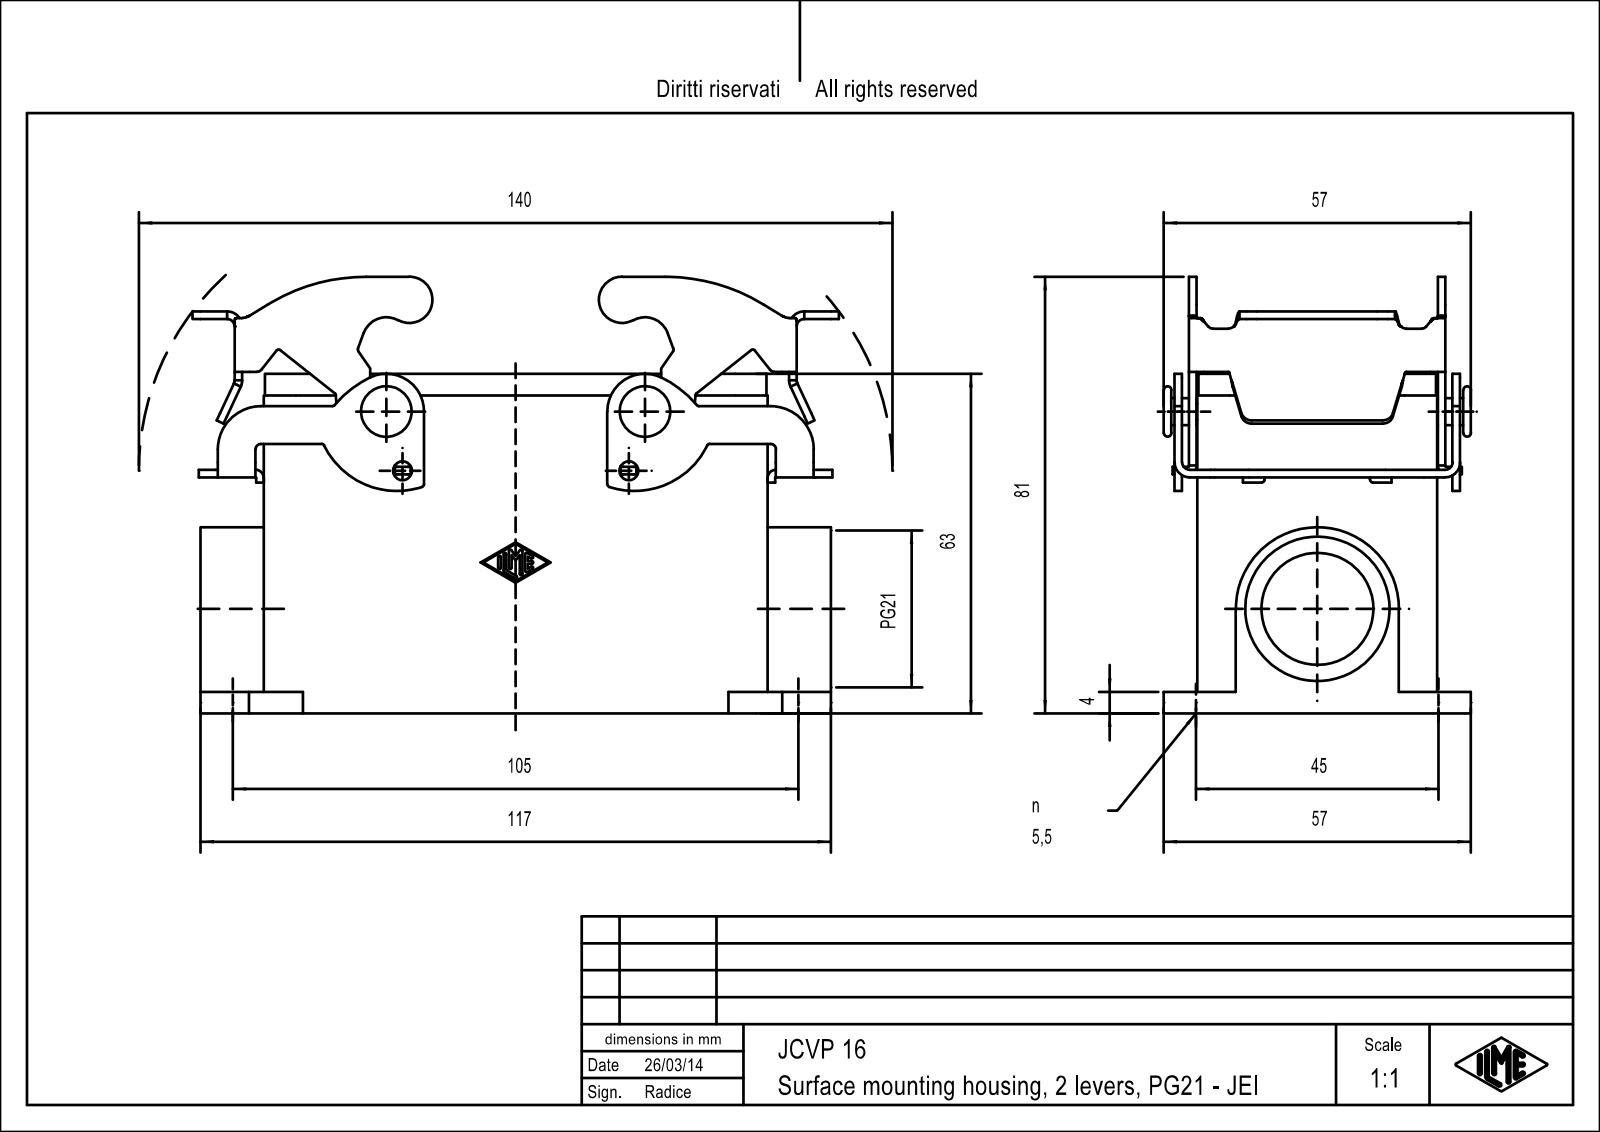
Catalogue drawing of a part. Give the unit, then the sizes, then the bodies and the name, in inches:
Units: inches
Overall size (bounding box): 4.723 × 3.189 × 2.244
Round holes (diameter × count): ⌀0.097 ×4, ⌀0.118 ×4, ⌀0.217 ×4, ⌀0.138 ×2, ⌀0.818 ×1, ⌀1.054 ×1
Round bosses / shafts (diameter × count): ⌀0.197 ×2, ⌀0.126 ×2, ⌀0.118 ×2
Partial cylindrical surfaces — rounded edges, fillets, slot ends (radius × count): R0.02 ×22, R0.039 ×18, R0.01 ×16, R0.059 ×14, R0.079 ×12, R0.055 ×10, R0.11 ×10, R0.315 ×6
Main face-to-face distances: 0.157, 1.594, 0.055, 1.752, 1.437, 0.106, 1.925, 0.061, 0.219, 1.656
Hole centre spacings: 0.647, 1.517, 3.61, 3.862, 1.063, 1.772, 3.051, 3.231
Volume: 6.8 in³ · Surface area: 97.24 in²
Bodies: 3 solids, 613 faces (293 planar, 272 cylindrical, 48 other)
Part name (STEP PRODUCT): p1; p2; p3; JCVP_16
STEP written by: Creo Elements/Direct Modeling 18.0B 02-Dec-2011 (C) Parametric Technology GmbH (AUTOMOTIVE_DESIGN)
